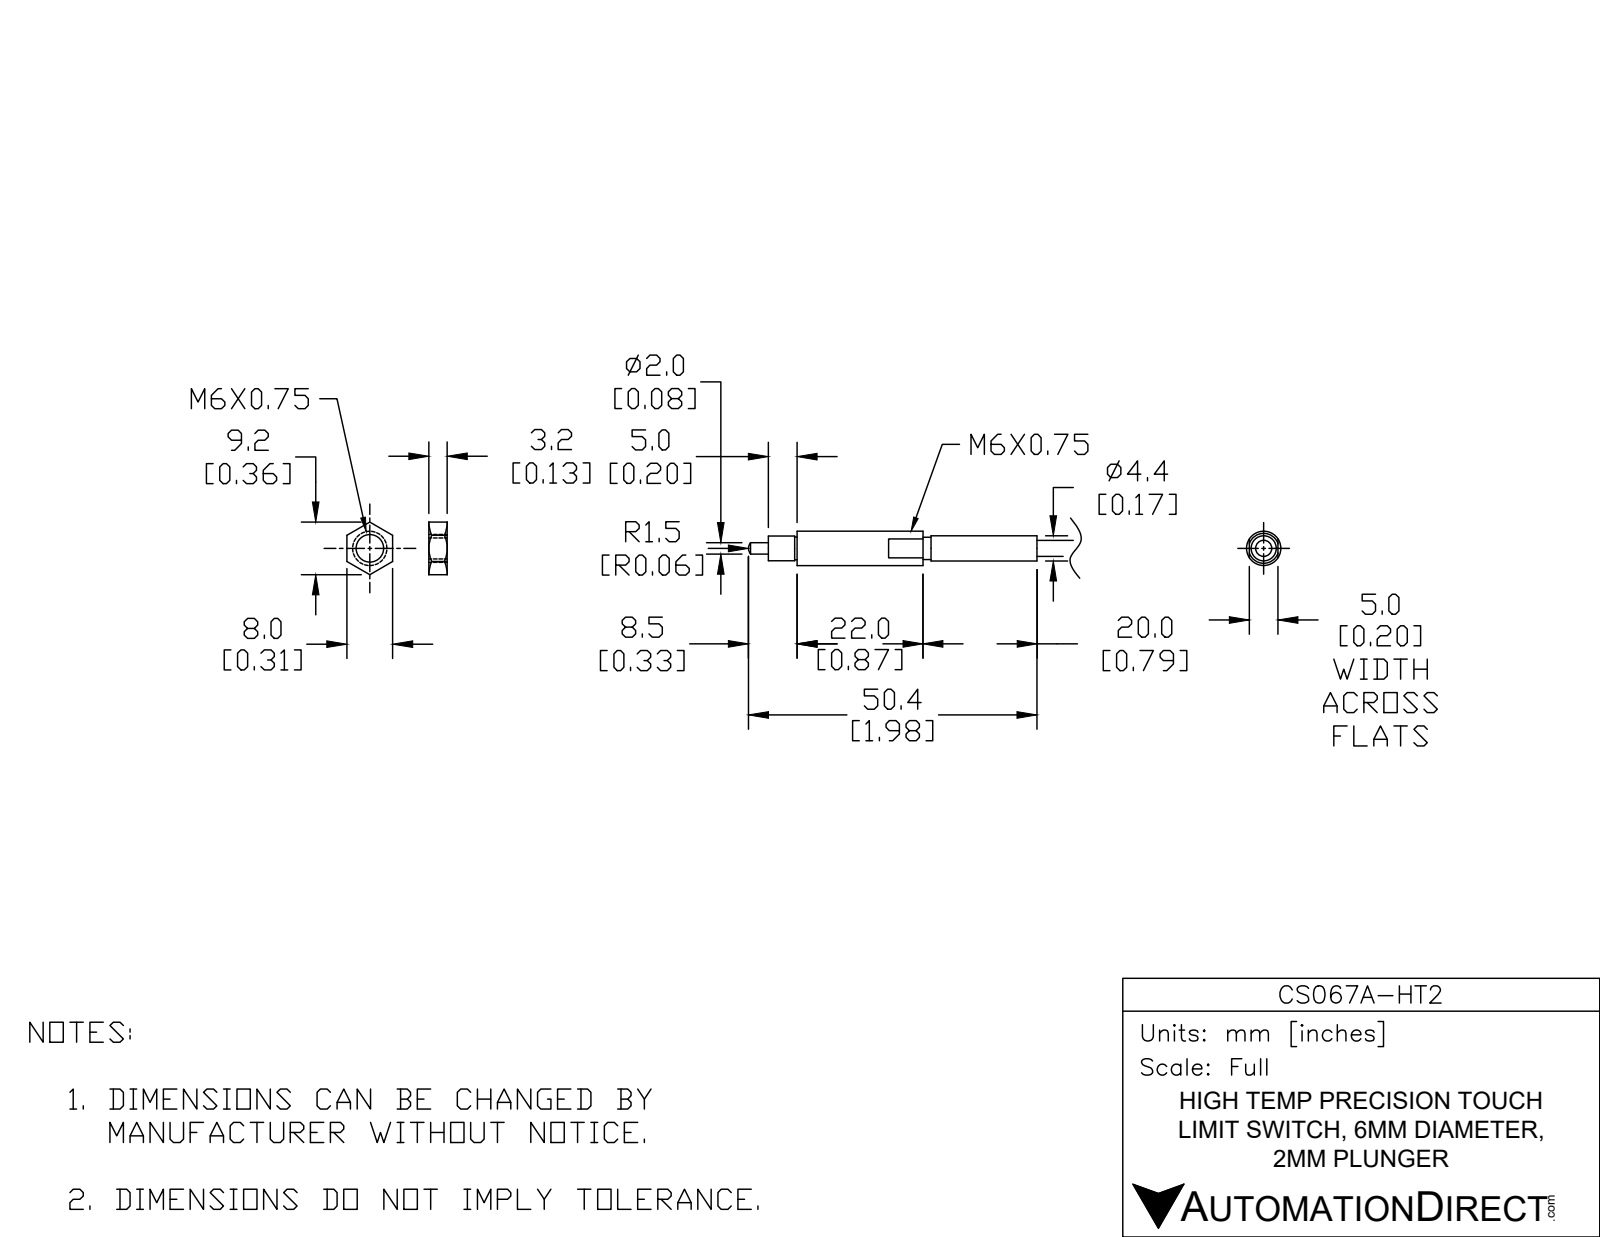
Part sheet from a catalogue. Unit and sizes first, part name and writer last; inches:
Units: inches
Overall size (bounding box): 2.299 × 0.236 × 0.236
Round bosses / shafts (diameter × count): ⌀0.236 ×1, ⌀0.173 ×1, ⌀0.169 ×1, ⌀0.157 ×1, ⌀0.154 ×1, ⌀0.11 ×1, ⌀0.079 ×1
Main face-to-face distances: 0.197, 0.866, 0.197, 1.063, 1.847, 1.65, 0.783, 2.162, 1.965, 1.098
Volume: 0.06 in³ · Surface area: 1.812 in²
Bodies: 1 solid, 189 faces (11 planar, 101 cylindrical, 77 other)
STEP written by: Spatial InterOp 3D (CONFIG_CONTROL_DESIGN)
